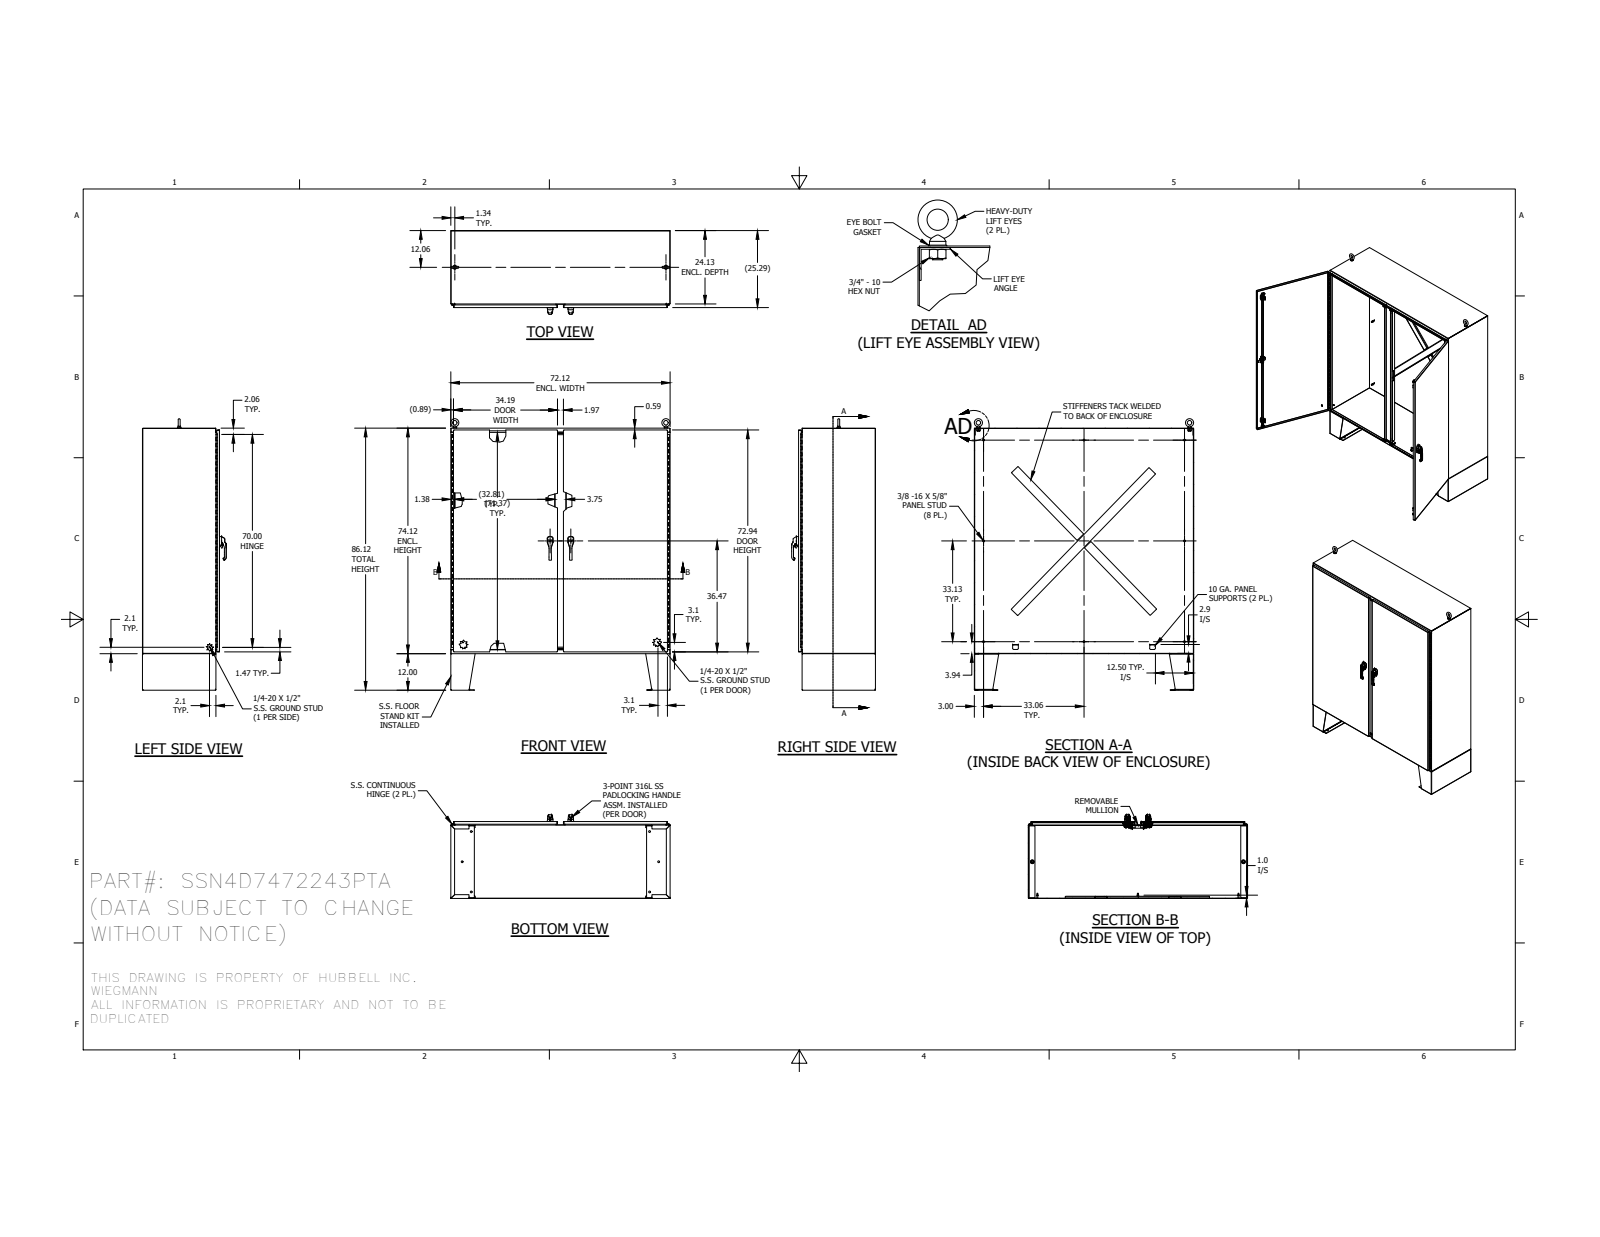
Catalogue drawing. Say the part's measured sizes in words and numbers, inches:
The part is named "HFW32451; HFW3762; LOCK-NUT_AF0; SSFK1224LG (+8 more)". Its 3-D file was written by "SolidWorks 2014 (AUTOMOTIVE_DESIGN)". It is 138 solids with 7352 faces: 2804 planar, 2832 cylindrical and 1716 other. Overall it measures 89.248 by 72.125 by 27.538 inches. Its volume is 2 122 cubic inches and its surface area 44 427 square inches. Round holes: 18 of diameter 0.563, 16 of diameter 0.262, 16 of diameter 0.375, 8 of diameter 0.187, 6 of diameter 0.213, 6 of diameter 0.25, 6 of diameter 0.281, 4 of diameter 0.196, 4 of diameter 0.241, 4 of diameter 0.252, 4 of diameter 0.281, 4 of diameter 0.315. Round bosses or shafts: 10 of diameter 0.33, 8 of diameter 0.625, 7 of diameter 0.25, 6 of diameter 1, 6 of diameter 0.533, 6 of diameter 0.236, 4 of diameter 0.563, 4 of diameter 0.531. Partial cylindrical surfaces (rounded edges, fillets, slot ends): 360 of radius 0.02, 213 of radius 0.012, 46 of radius 0.019, 46 of radius 0.125, 34 of radius 0.05, 32 of radius 0.031, 28 of radius 0.079, 24 of radius 0.025. The main face-to-face distances are 0.094, 25.193, 25.196, 72.031, 74.031, 25.1, 25.102, 25.287, 0.091, 25.29. The hole center spacings are 15.556, 0.38, 0.38, 0.76, 7.778, 31.111, 64.052, 64.427.
